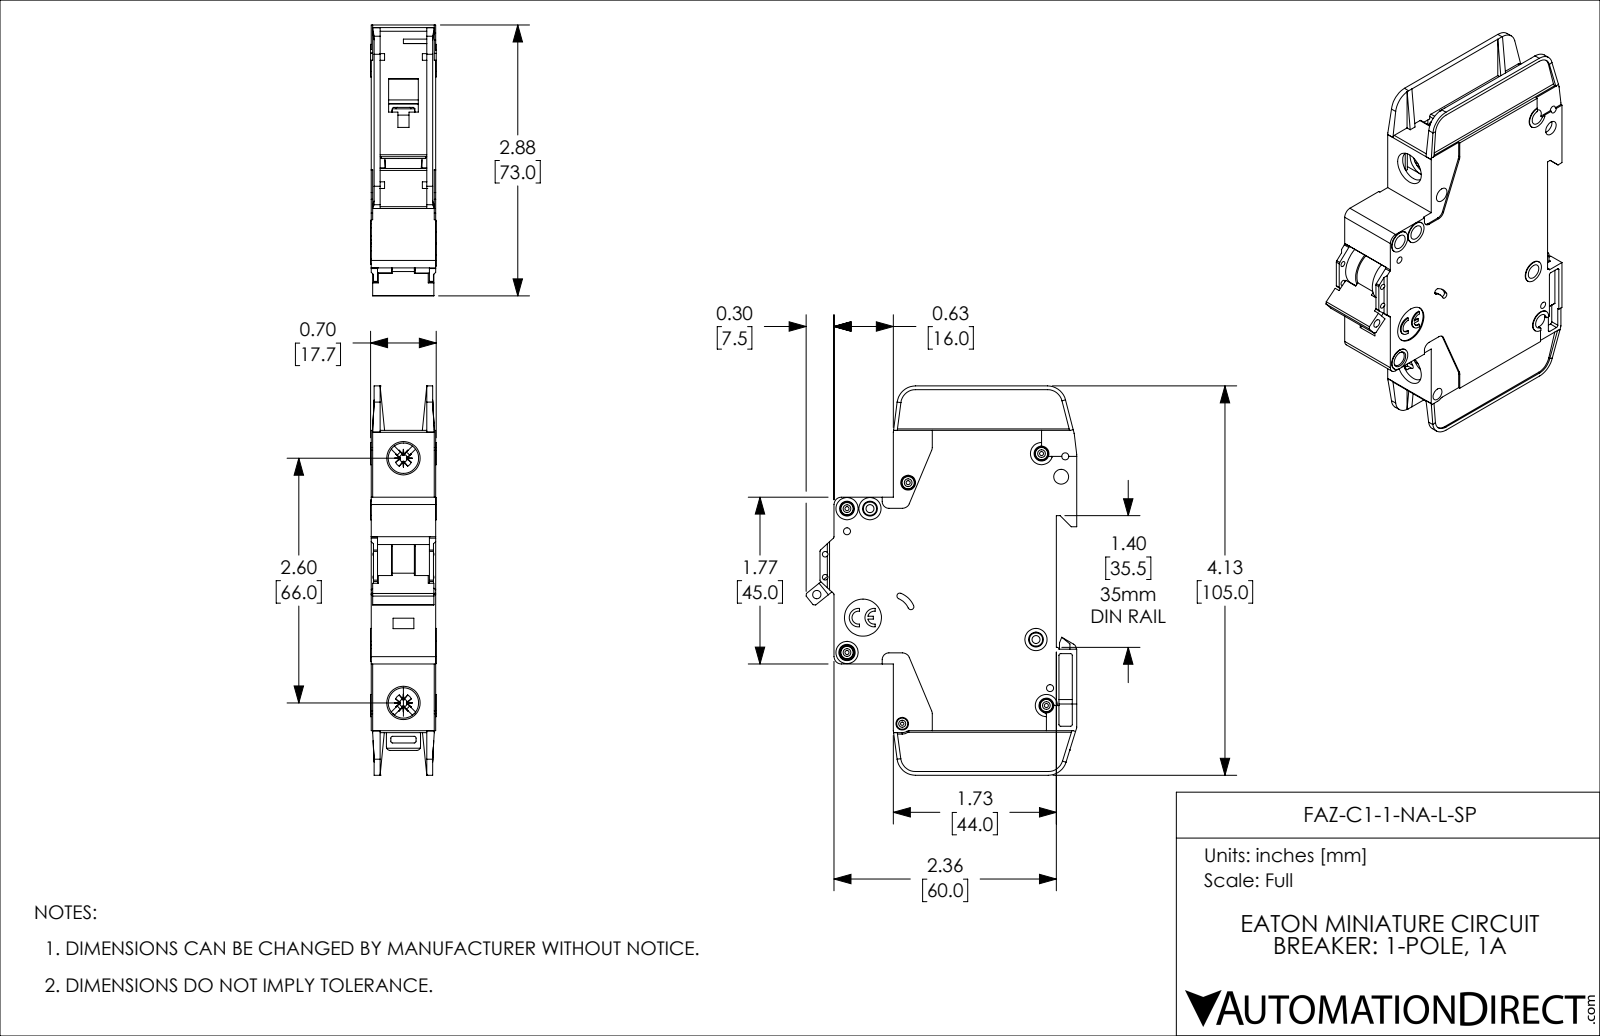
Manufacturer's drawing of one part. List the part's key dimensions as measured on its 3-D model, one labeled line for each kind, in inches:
Part name (STEP PRODUCT): FAZ-C1-1-NA-L-SP
STEP written by: SolidWorks 2019 (AUTOMOTIVE_DESIGN)
Units: inches
Bodies: 1 solid, 1127 faces (671 planar, 357 cylindrical, 99 other)
Overall size (bounding box): 4.134 × 2.876 × 0.697
Volume: 4.682 in³ · Surface area: 41.01 in²
Round holes (diameter × count): ⌀0.157 ×8, ⌀0.043 ×5, ⌀0.075 ×4, ⌀0.059 ×2, ⌀0.085 ×2, ⌀0.323 ×2, ⌀0.035 ×1, ⌀0.089 ×1, ⌀0.098 ×1, ⌀0.134 ×1, ⌀0.394 ×1
Round bosses / shafts (diameter × count): ⌀0.13 ×5, ⌀0.236 ×4, ⌀0.118 ×2, ⌀0.098 ×1
Partial cylindrical surfaces — rounded edges, fillets, slot ends (radius × count): R0.02 ×42, R0.016 ×10, R0.039 ×10, R0.079 ×8, R0.197 ×5, R0.008 ×4, R0.026 ×4, R0.043 ×4
Main face-to-face distances: 0.047, 0.685, 0.591, 0.638, 0.094, 0.543, 0.016, 0.031, 0.496, 0.575
Hole centre spacings: 0.244, 0.537, 0.87, 0.189, 0.199, 0.204, 0.221, 0.24
